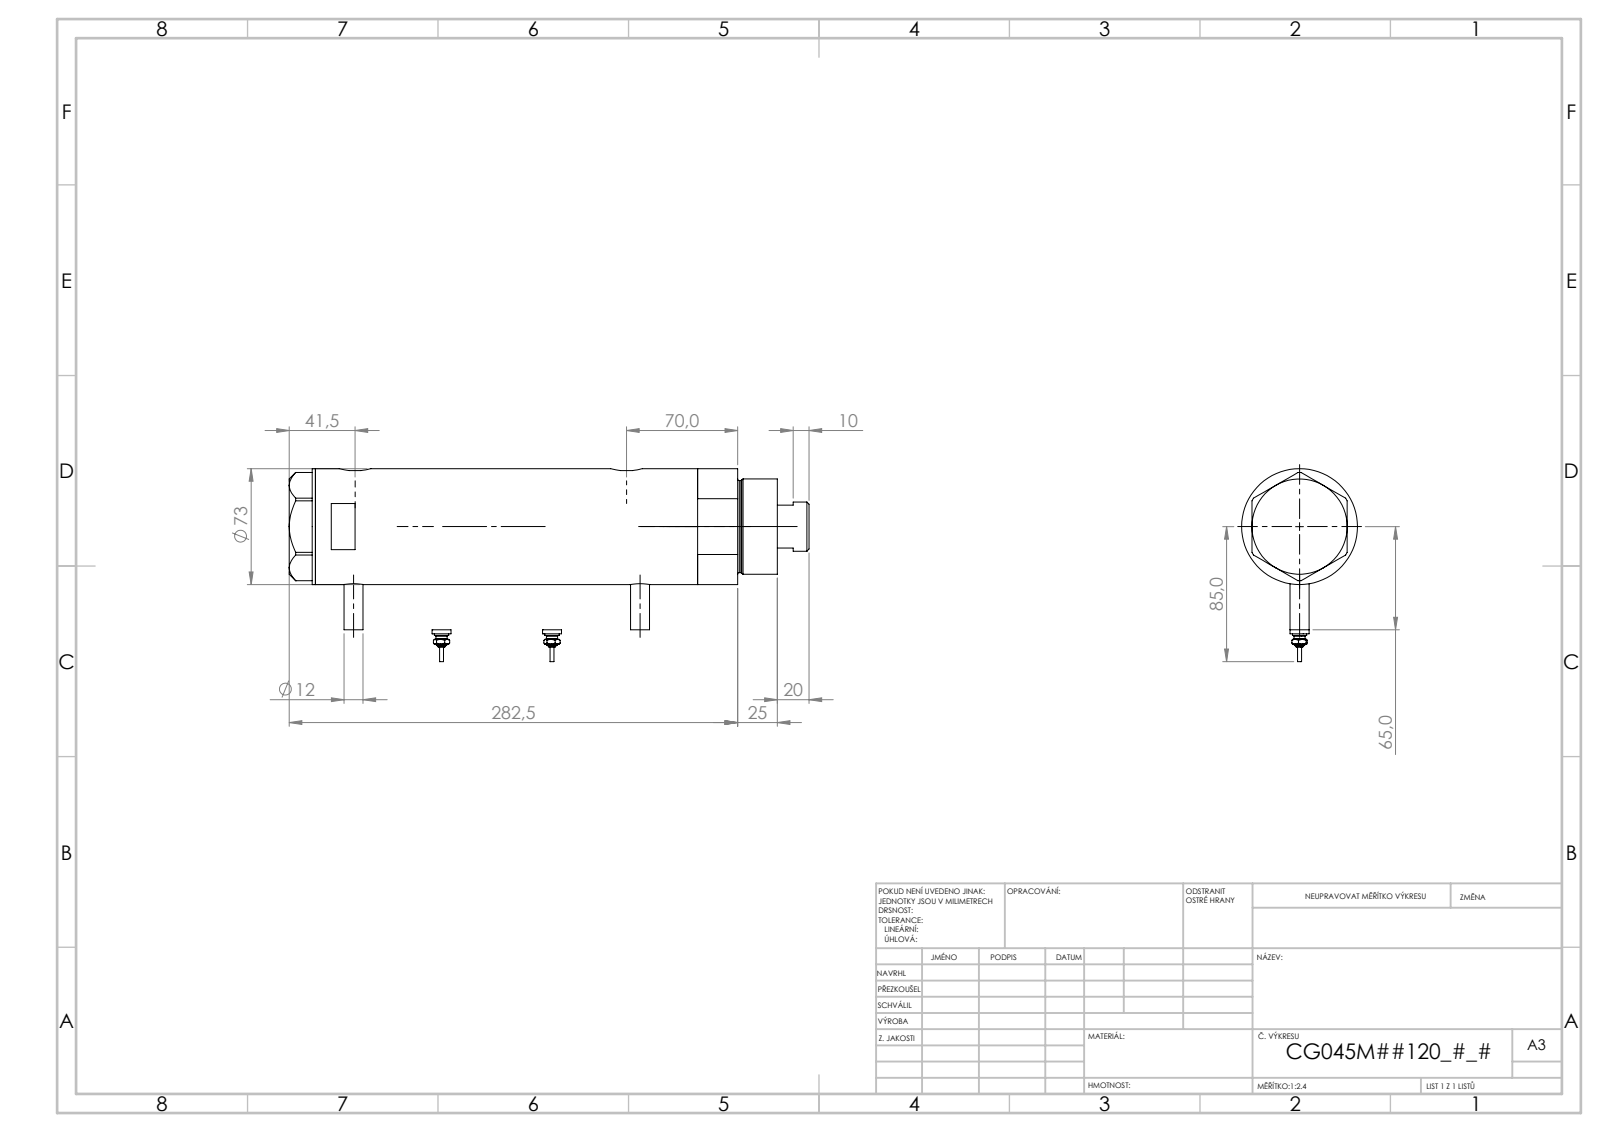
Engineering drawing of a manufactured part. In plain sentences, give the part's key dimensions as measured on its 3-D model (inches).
The part is named "V270CG_VC; V270CG_SWITCH; V270CG_MIDDLE; V270CG_FRONT (+1 more)". Its 3-D file was written by "SolidWorks 2019 (CONFIG_CONTROL_DESIGN)". It is 6 solids with 231 faces: 78 planar, 79 cylindrical and 74 other. Overall it measures 12.265 by 4.146 by 2.874 inches. Its volume is 65.78 cubic inches and its surface area 276.6 square inches. Round holes: 2 of diameter 0.197, 2 of diameter 0.492, 2 of diameter 0.518, 1 of diameter 0.413, 1 of diameter 1.26, 1 of diameter 1.319, 1 of diameter 1.772, 1 of diameter 1.89, 1 of diameter 2.52. Round bosses or shafts: 3 of diameter 0.472, 2 of diameter 0.354, 2 of diameter 0.276, 2 of diameter 0.171, 2 of diameter 0.094, 1 of diameter 2.874, 1 of diameter 2.362, 1 of diameter 2.283. Partial cylindrical surfaces (rounded edges, fillets, slot ends): 2 of radius 0.394. The main face-to-face distances are 7.368, 1.024, 6.344, 0.65, 1.673, 8.017, 10.827, 11.477, 9.804, 3.459. The hole center spacings are 6.758, 0.039, 0.039, 0.335, 0.335, 6.384, 6.423, 6.423.
